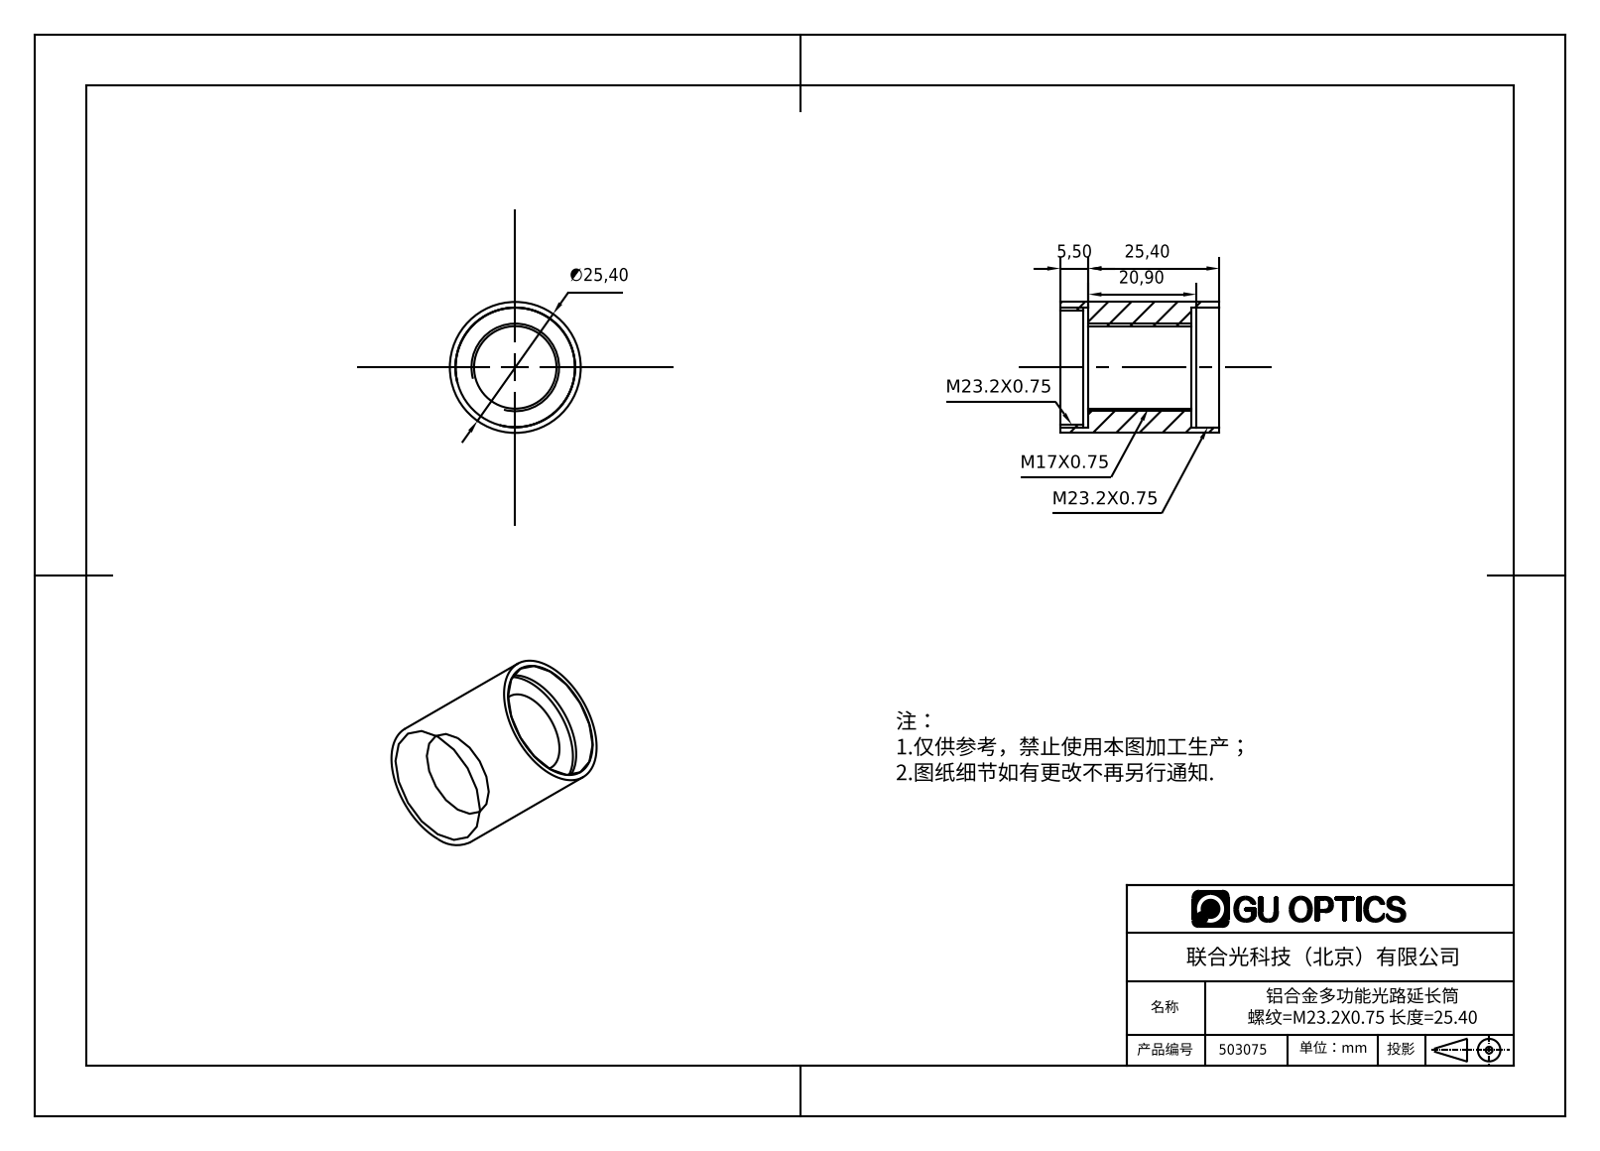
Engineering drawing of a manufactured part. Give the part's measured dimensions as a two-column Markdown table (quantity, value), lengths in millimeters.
| quantity | value |
| --- | --- |
| part name | 503075 |
| STEP written by | SolidWorks 2016 (AUTOMOTIVE_DESIGN) |
| units | millimeters |
| bodies | 1 solid, 18 faces (6 planar, 12 cylindrical, 0 other) |
| overall size | 30.9 × 25.4 × 25.4 |
| volume | 7 152 mm³ |
| surface area | 4 967 mm² |
| round holes (diameter × count) | 16 × 1, 22.2 × 1, 23.2 × 1, 23.4 × 1 |
| round bosses / shafts (diameter × count) | 25.4 × 1 |
| main face-to-face distances | 19.9, 5.5, 25.4, 30.9, 4.5, 26.4, 1, 20.9, 21.9 |
